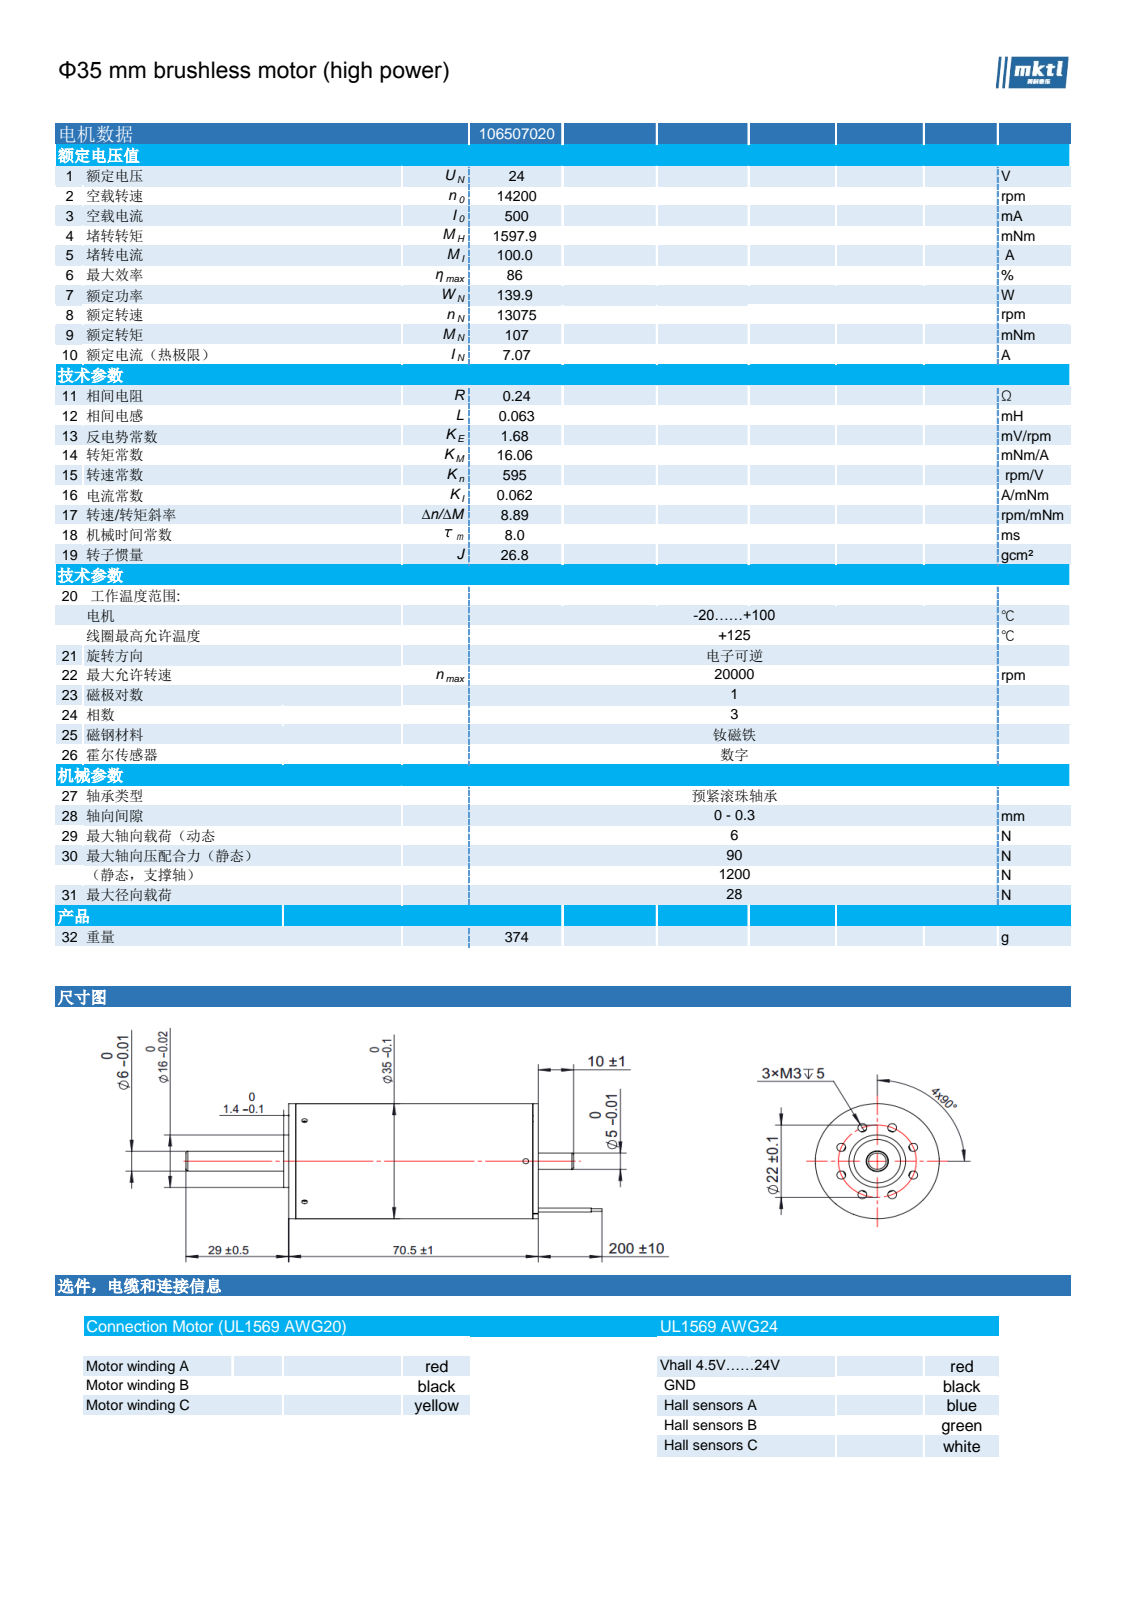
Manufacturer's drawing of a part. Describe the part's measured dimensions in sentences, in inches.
The part is named "106507020". Its 3-D file was written by "SolidWorks 2025 (AUTOMOTIVE_DESIGN)". It is 324 solids with 2956 faces: 1261 planar, 1539 cylindrical and 156 other. Overall it measures 4.626 by 1.378 by 1.378 inches. Its volume is 3.858 cubic inches and its surface area 410.9 square inches. Round holes: 8 of diameter 0.098, 6 of diameter 0.083, 5 of diameter 0.03, 4 of diameter 0.039, 3 of diameter 0.059, 3 of diameter 0.063, 3 of diameter 0.118, 2 of diameter 0.049, 1 of diameter 0.374, 1 of diameter 0.394, 1 of diameter 0.512, 1 of diameter 0.52. Round bosses or shafts: 6 of diameter 0.023, 5 of diameter 0.039, 5 of diameter 0.024, 3 of diameter 0.157, 3 of diameter 0.063, 3 of diameter 0.047, 3 of diameter 0.031, 1 of diameter 1.378. Partial cylindrical surfaces (rounded edges, fillets, slot ends): 24 of radius 0.004, 11 of radius 0.03, 8 of radius 0.017, 5 of radius 0.012, 4 of radius 0.039, 4 of radius 0.079, 2 of radius 0.02, 1 of radius 0.196. The main face-to-face distances are 0.016, 0.024, 0.031, 0.039, 0.047, 0.055, 0.063, 0.071, 0.079, 0.087. The hole center spacings are 0.433, 0.612, 0.8, 0.522, 0.079, 0.331, 0.331, 0.866.
